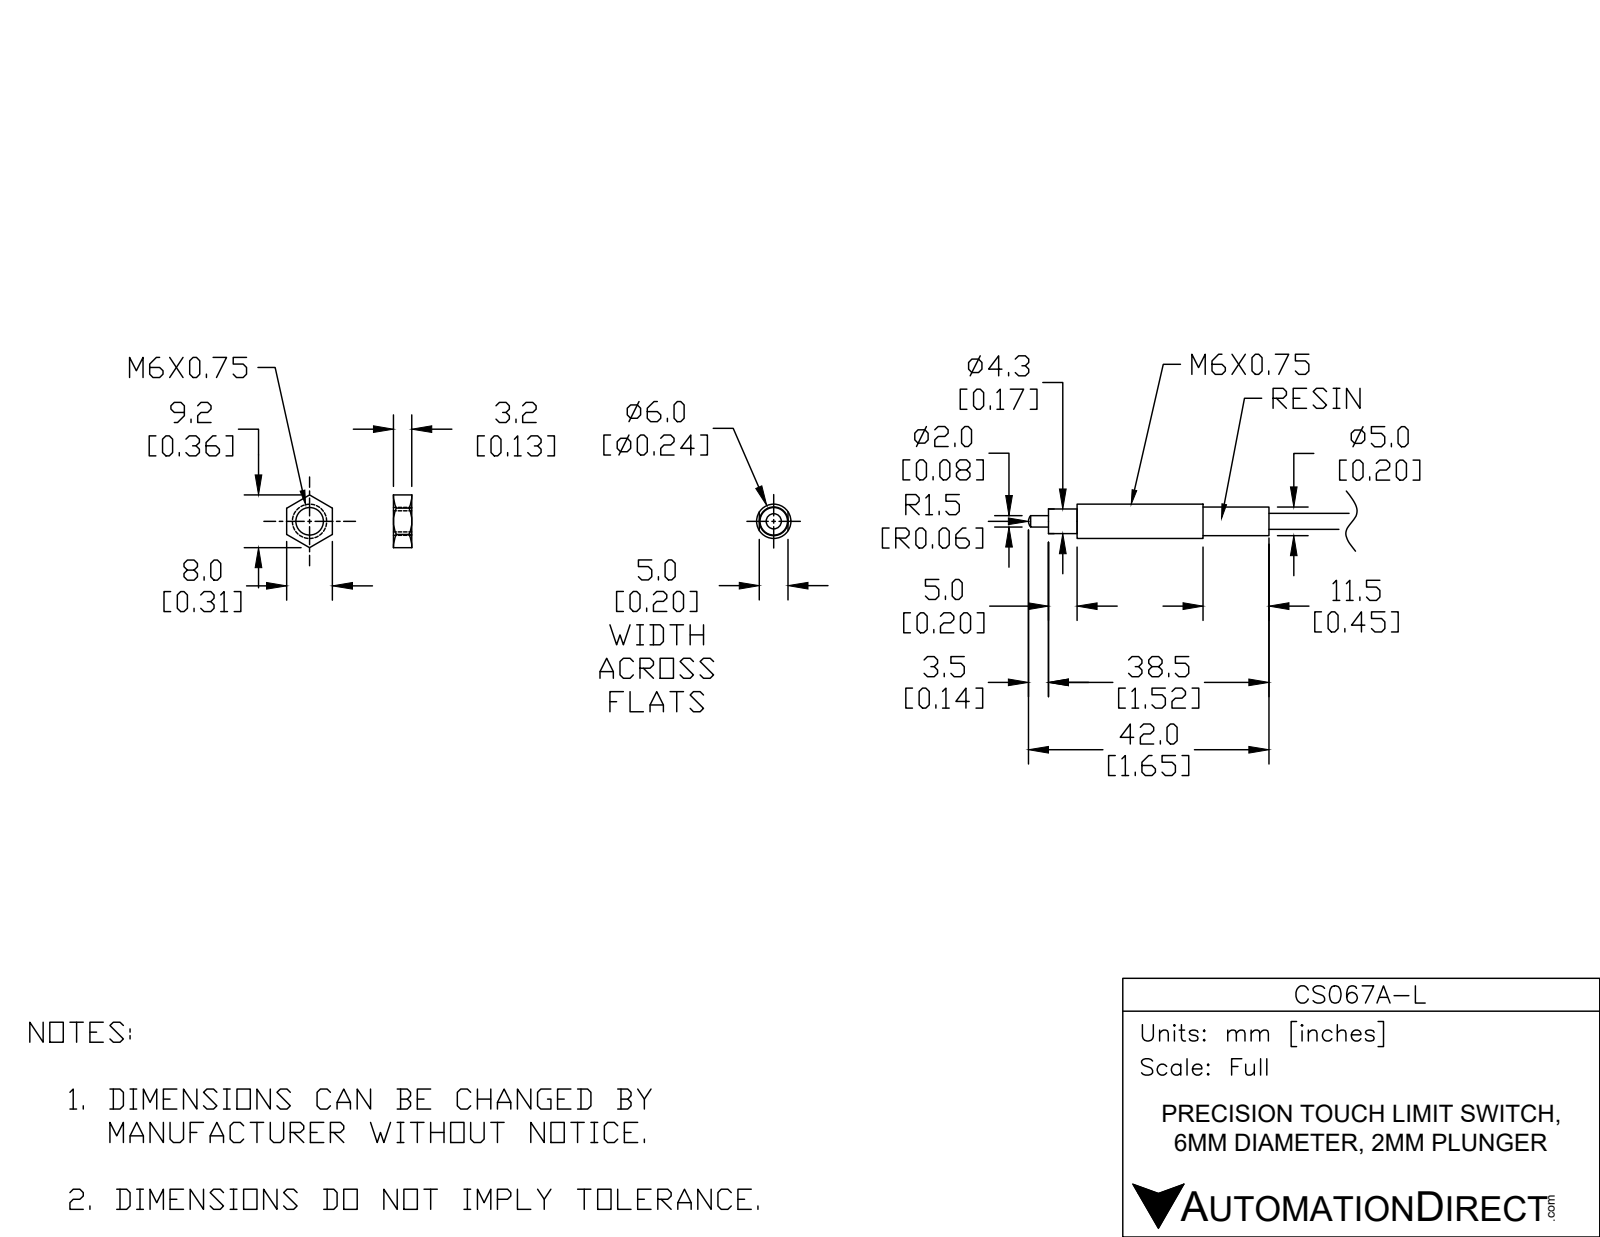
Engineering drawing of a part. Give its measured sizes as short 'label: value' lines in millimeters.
name: CS067A-L
written by: SolidWorks 2017 (AUTOMOTIVE_DESIGN)
unit: mm
bodies: 1 solid, 183 faces (11 planar, 97 cylindrical, 75 other)
size: 56 × 6 × 6
volume: 950 mm³; area: 1 121 mm²
bosses: 1× ⌀6, 1× ⌀5, 1× ⌀4.3, 1× ⌀2.8, 1× ⌀2
face distances: 5, 38.5, 33.5, 25.5, 27, 52.5, 47.5, 14, 22, 11.5
